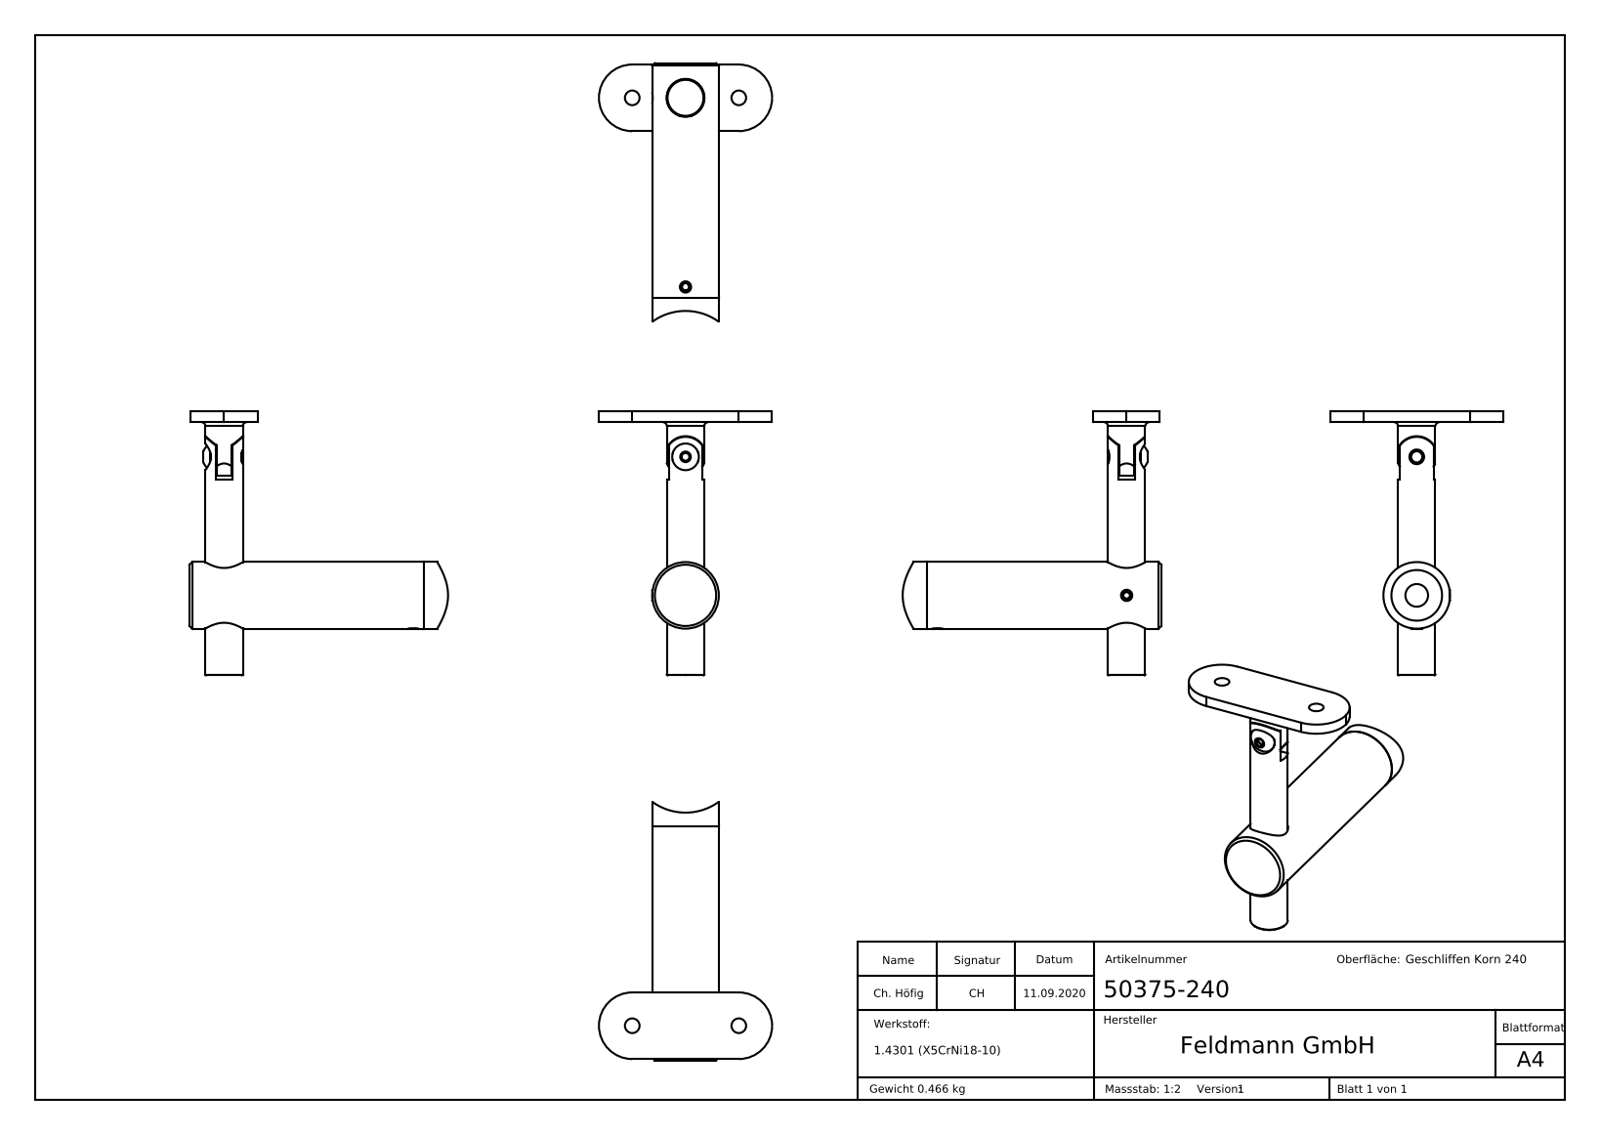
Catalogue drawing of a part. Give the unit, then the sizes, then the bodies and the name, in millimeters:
Units: millimetres
Overall size (bounding box): 99 × 97.08 × 88
Round holes (diameter × count): ⌀4.2 ×3, ⌀5.5 ×3, ⌀8.5 ×1, ⌀10 ×1, ⌀14.2 ×1, ⌀16 ×1, ⌀19 ×1
Round bosses / shafts (diameter × count): ⌀5 ×3, ⌀25 ×1, ⌀14 ×1
Partial cylindrical surfaces — rounded edges, fillets, slot ends (radius × count): R7.75 ×3, R12.5 ×2, R8.1 ×1, R21.2 ×1
Main face-to-face distances: 4, 88, 9.5, 15.5, 9.75, 5.75, 15.25, 25.5, 3, 91
Hole centre spacings: 20, 73.76, 40, 52, 71
Volume: 59 031 mm³ · Surface area: 21 952 mm²
Bodies: 7 solids, 368 faces (147 planar, 78 cylindrical, 143 other)
Part name (STEP PRODUCT): 5037X-240 Teil4_50375-240 Teil4; DIN 7380_DIN 7380 M5x12; DIN913; 5037X-240 Teil1 (+8 more)
STEP written by: SolidWorks 2018 (CONFIG_CONTROL_DESIGN)
